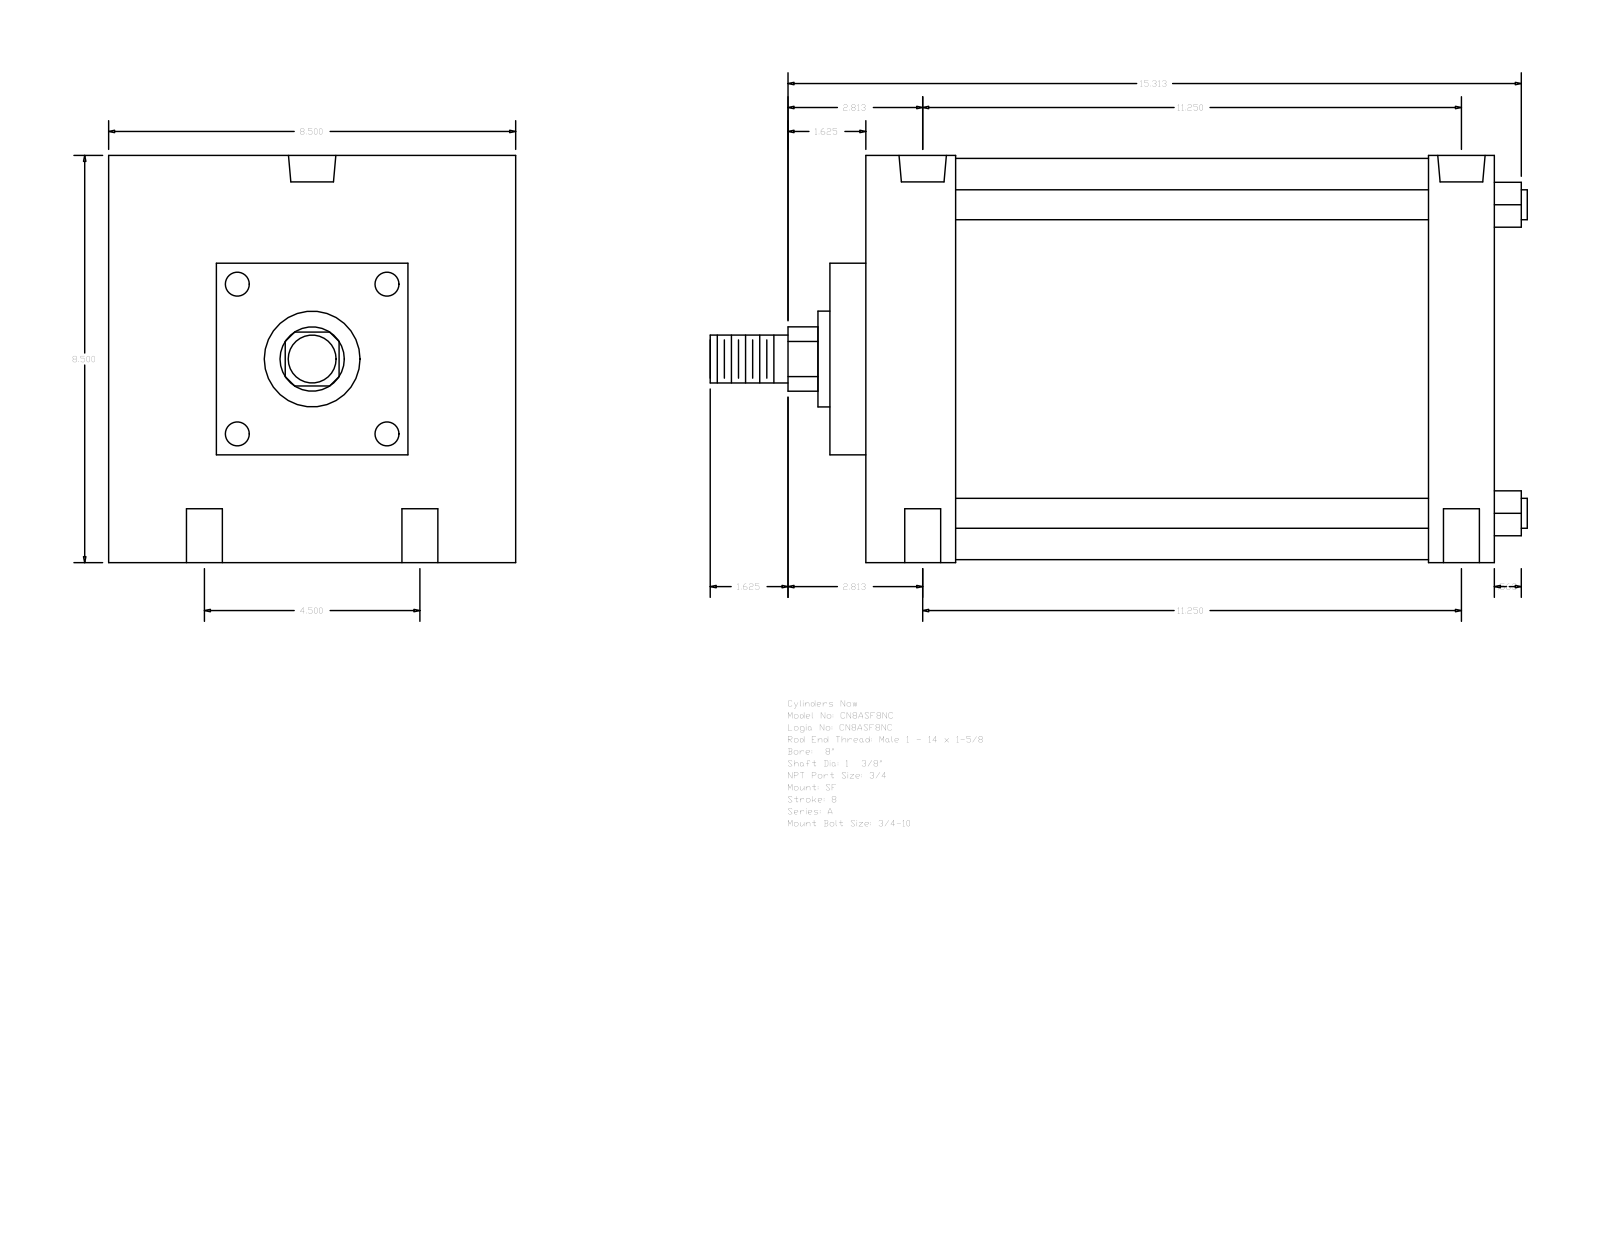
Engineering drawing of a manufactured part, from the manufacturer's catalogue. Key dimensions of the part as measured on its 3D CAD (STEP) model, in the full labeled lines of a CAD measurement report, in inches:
Part name (STEP PRODUCT): A_SF__0800_1.375
STEP written by: GSSL Pune (CONFIG_CONTROL_DESIGN)
Units: inches
Bodies: 0 solids, 93 faces (67 planar, 26 cylindrical, 0 other)
Overall size (bounding box): 17.063 × 8.5 × 8.5
Round holes (diameter × count): ⌀0.75 ×4, ⌀0.594 ×2, ⌀0.989 ×2
Round bosses / shafts (diameter × count): ⌀0.625 ×4, ⌀8.375 ×1, ⌀2 ×1, ⌀1.375 ×1, ⌀1 ×1
Partial cylindrical surfaces — rounded edges, fillets, slot ends (radius × count): R0.672 ×1
Main face-to-face distances: 13.125, 8.5, 1.875, 11.75, 9.875, 11.25, 1.375, 0.75, 2.625, 12.5
Hole centre spacings: 2.25, 11.473, 11.25, 4.5, 12.117, 10.75
